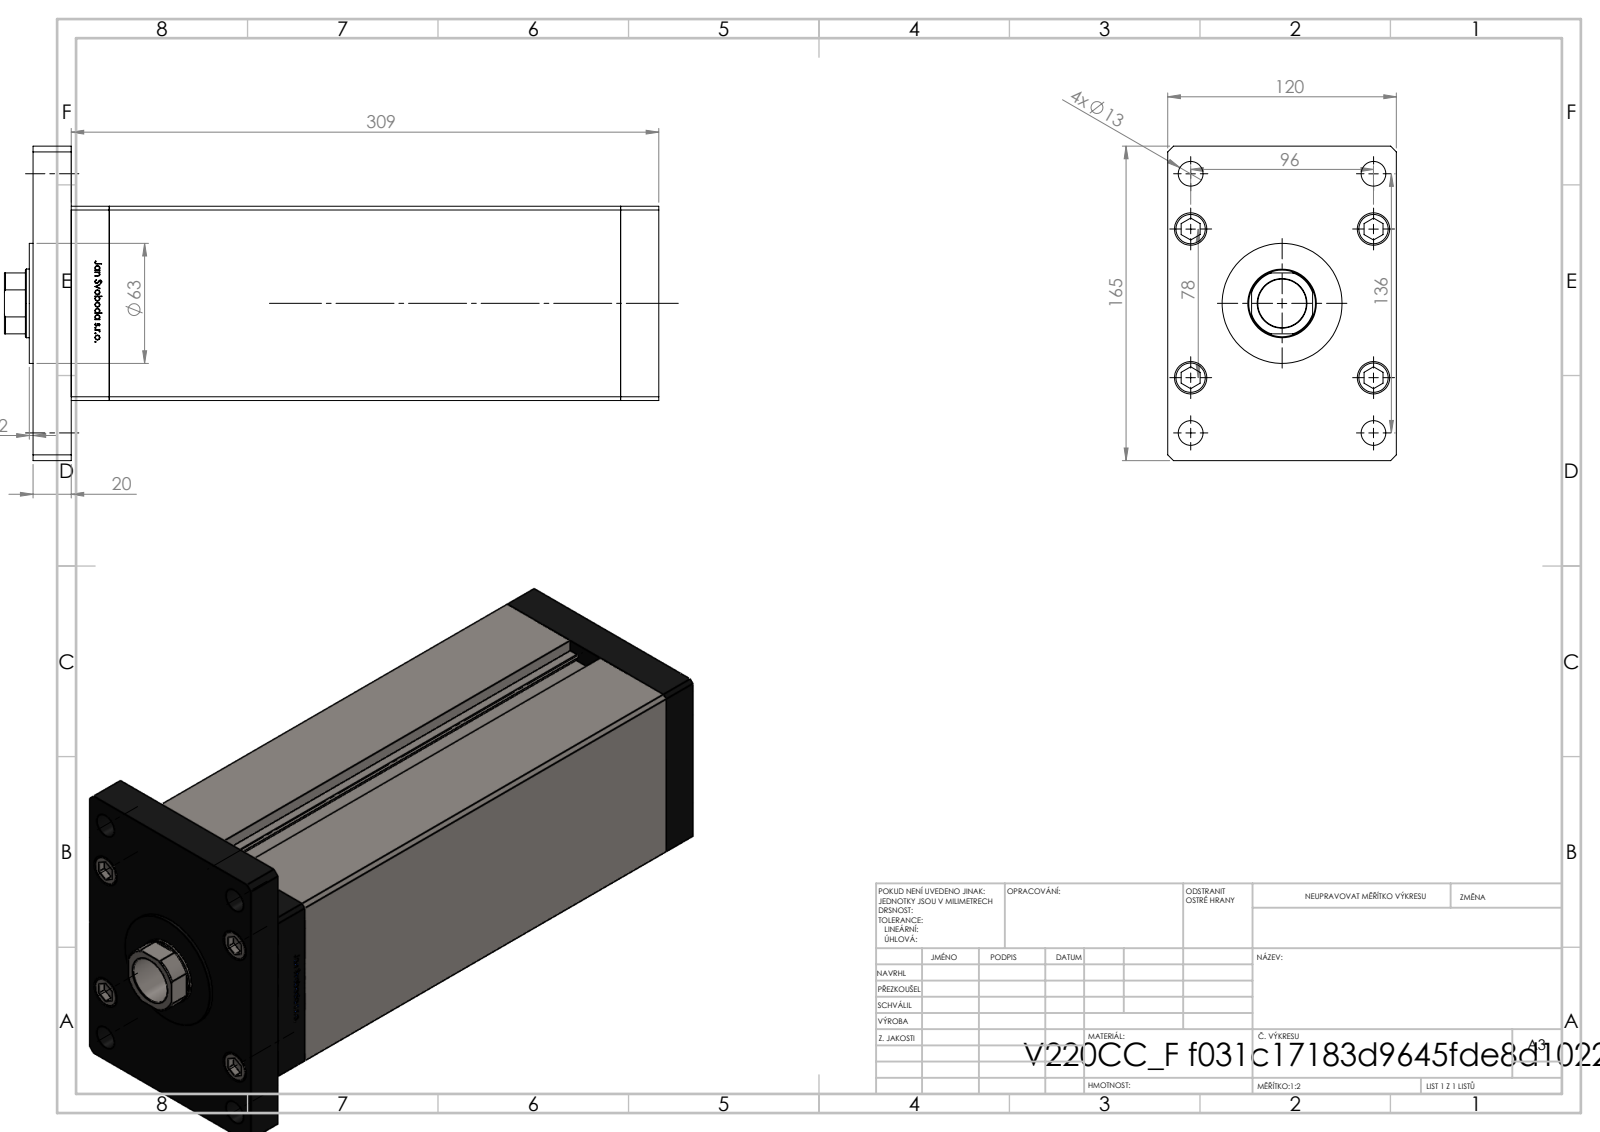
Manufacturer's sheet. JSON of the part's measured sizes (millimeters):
{"part_name": "V220C BACK_F; V220C_F; V220C_VC_F; V220C_FRONT_F (+2 more)", "step_written_by": "SolidWorks 2019 (CONFIG_CONTROL_DESIGN)", "units": "millimeters", "bodies": {"solids": 19, "faces": 1311, "planar": 517, "cylindrical": 188, "other": 606}, "overall_size": [343.5, 165, 120], "volume_mm3": 3609000, "surface_area_mm2": 414391, "round_holes": [[13.5, 5], [18, 5], [12, 4], [13, 4], [17, 4], [2, 2], [13.16, 2], [25.5, 1], [36, 1], [37.5, 1]], "round_bosses_or_shafts": [[8, 9], [17, 5], [63, 1]], "partial_cylinders_radius": [[0.93, 2], [17.5, 1]], "face_to_face_distances": [20, 120, 102, 288.5, 308.5, 268.5, 40, 328.5, 34.25, 42], "hole_center_spacings": [41.5, 29, 61.85, 83.23, 96, 100.28, 107, 143.75]}
